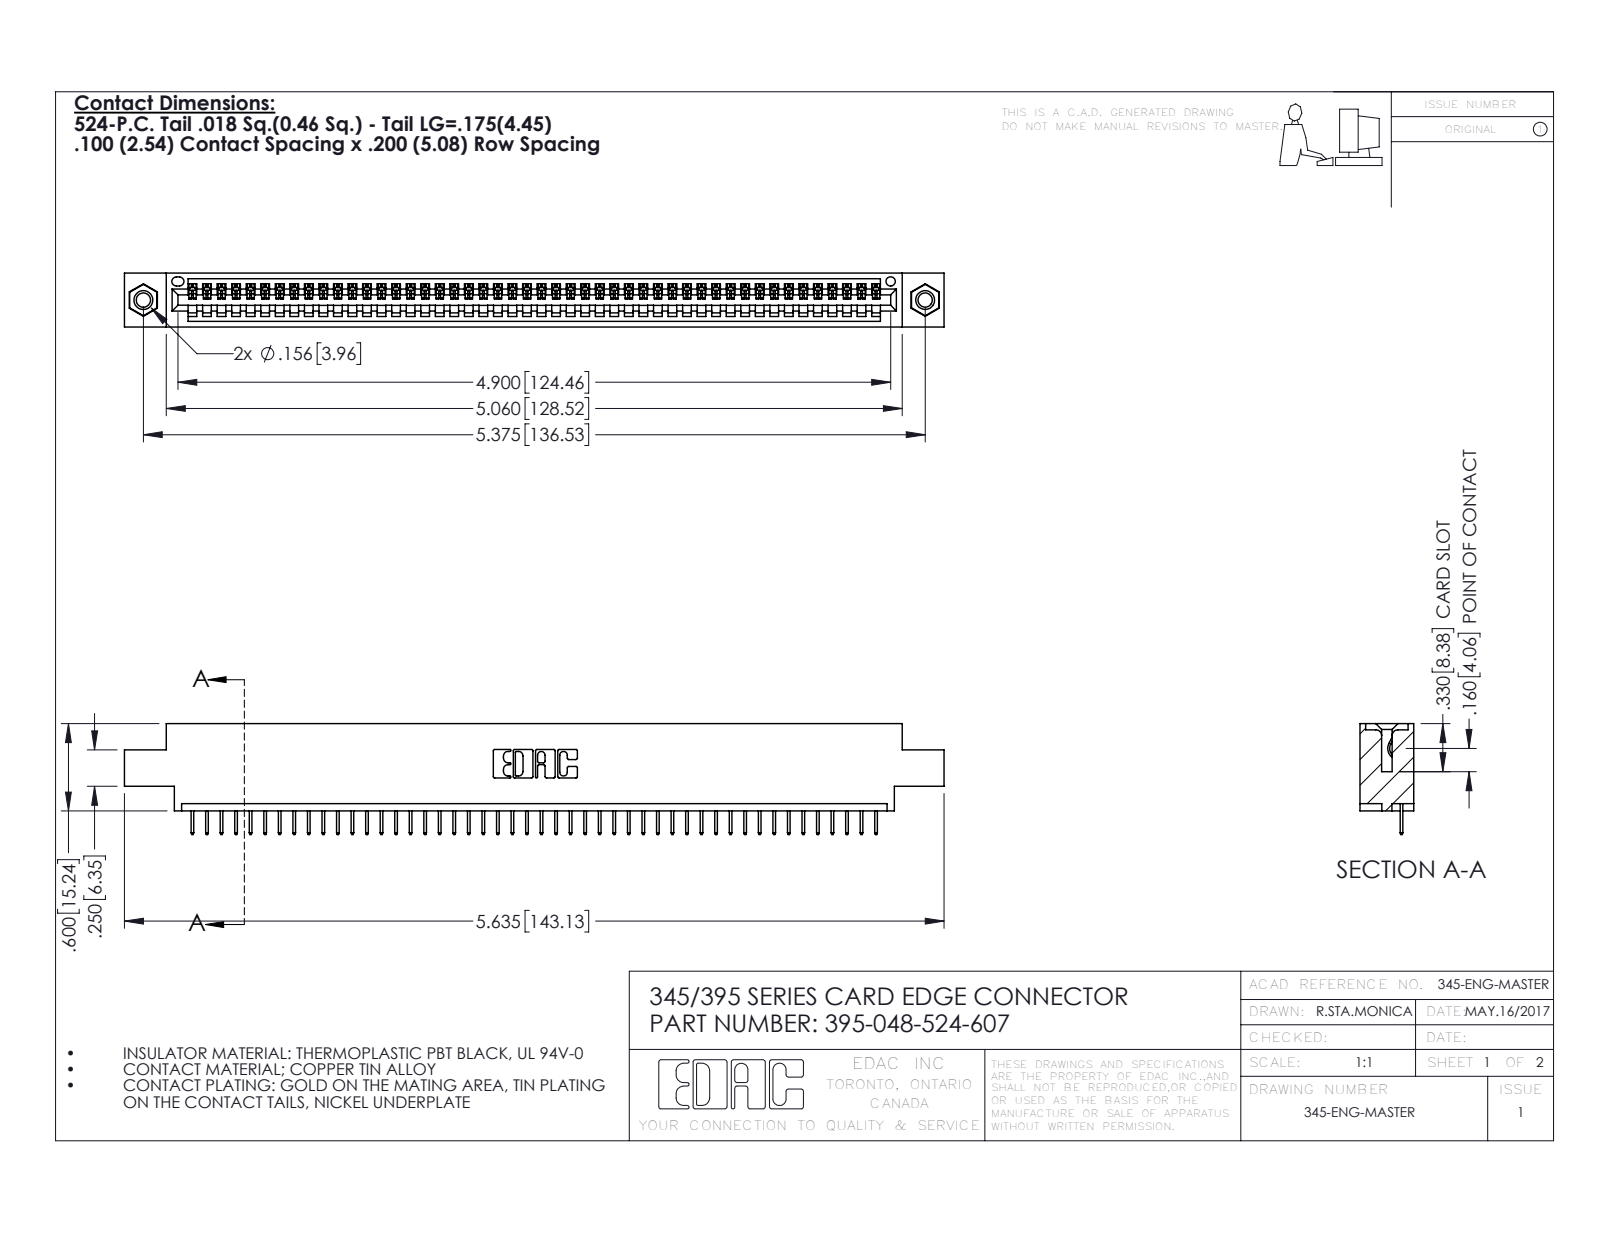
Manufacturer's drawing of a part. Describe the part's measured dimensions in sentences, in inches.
The part is named "395-048-524-607; 345-292-001_345-293-124; 345-250-001_345-250-005-103; 345 Part_0.170 Offset - 0.156 Dia-TI". Its 3-D file was written by "SolidWorks 2016 (CONFIG_CONTROL_DESIGN)". It is 51 solids with 3166 faces: 2324 planar, 826 cylindrical and 16 other. Overall it measures 5.635 by 0.762 by 0.37 inches. Its volume is 0.813 cubic inches and its surface area 26.88 square inches. Round holes: 2 of diameter 0.098, 2 of diameter 0.125, 2 of diameter 0.156, 1 of diameter 0.064. Round bosses or shafts: 2 of diameter 0.155. Partial cylindrical surfaces (rounded edges, fillets, slot ends): 96 of radius 0.006, 22 of radius 0.01, 6 of radius 0.007, 6 of radius 0.031, 3 of radius 0.026, 2 of radius 0.031, 2 of radius 0.04, 1 of radius 0.014. The main face-to-face distances are 0.072, 0.298, 0.37, 0.2, 0.098, 0.272, 0.025, 0.225, 0.072, 0.175. The hole center spacings are 0.27, 5.139, 5.375.
